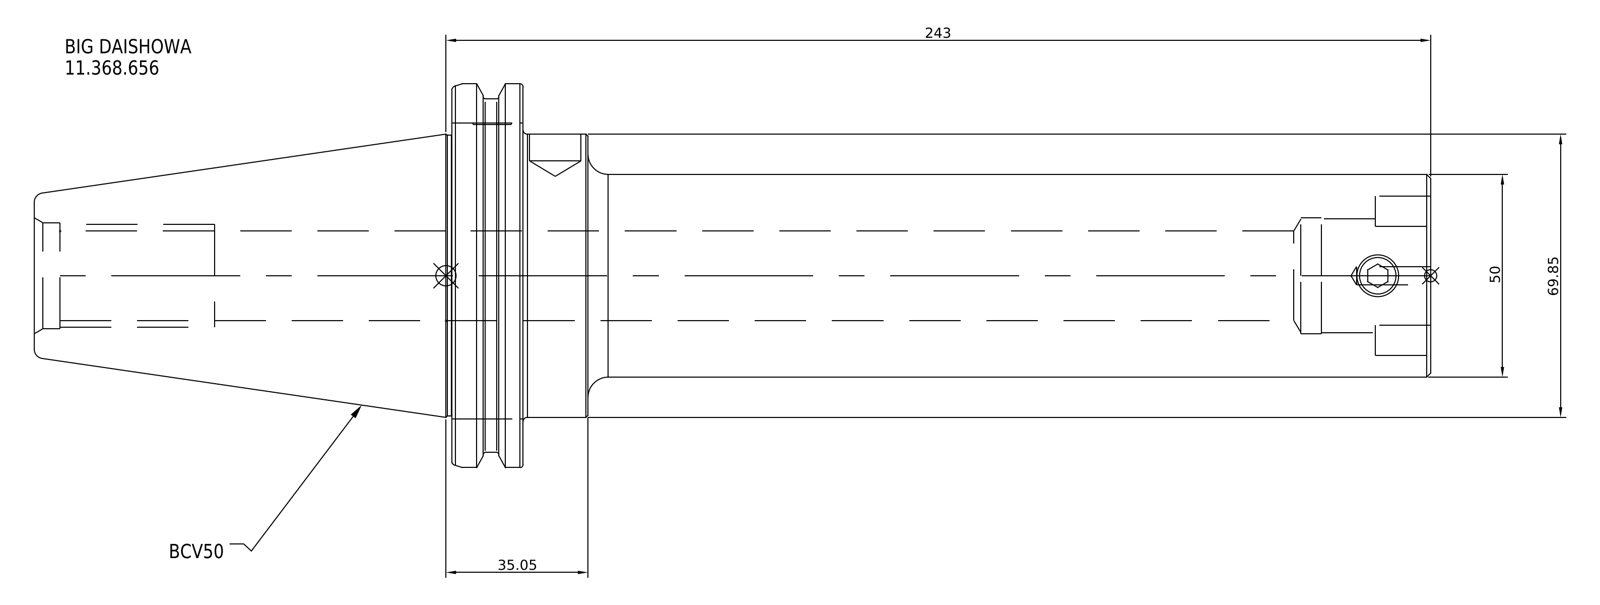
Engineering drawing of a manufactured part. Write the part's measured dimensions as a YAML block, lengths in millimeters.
part_name: "11.368.656"
step_written_by: "SolidWorks 2021 (CONFIG_CONTROL_DESIGN)"
units: millimeters
bodies: {solids: 1, faces: 16, planar: 7, cylindrical: 6, other: 3}
overall_size: [344.6, 98.43, 98.43]
volume: 850888
surface_area: 73646
round_bosses_or_shafts:
  - {diameter: 98.43, count: 1}
  - {diameter: 91.29, count: 1}
  - {diameter: 69.85, count: 1}
  - {diameter: 50, count: 1}
face_to_face_distances: [17.55, 223.95, 241.5, 208, 15.95, 33.5, 344.6, 136.6, 120.65, 103.1]
